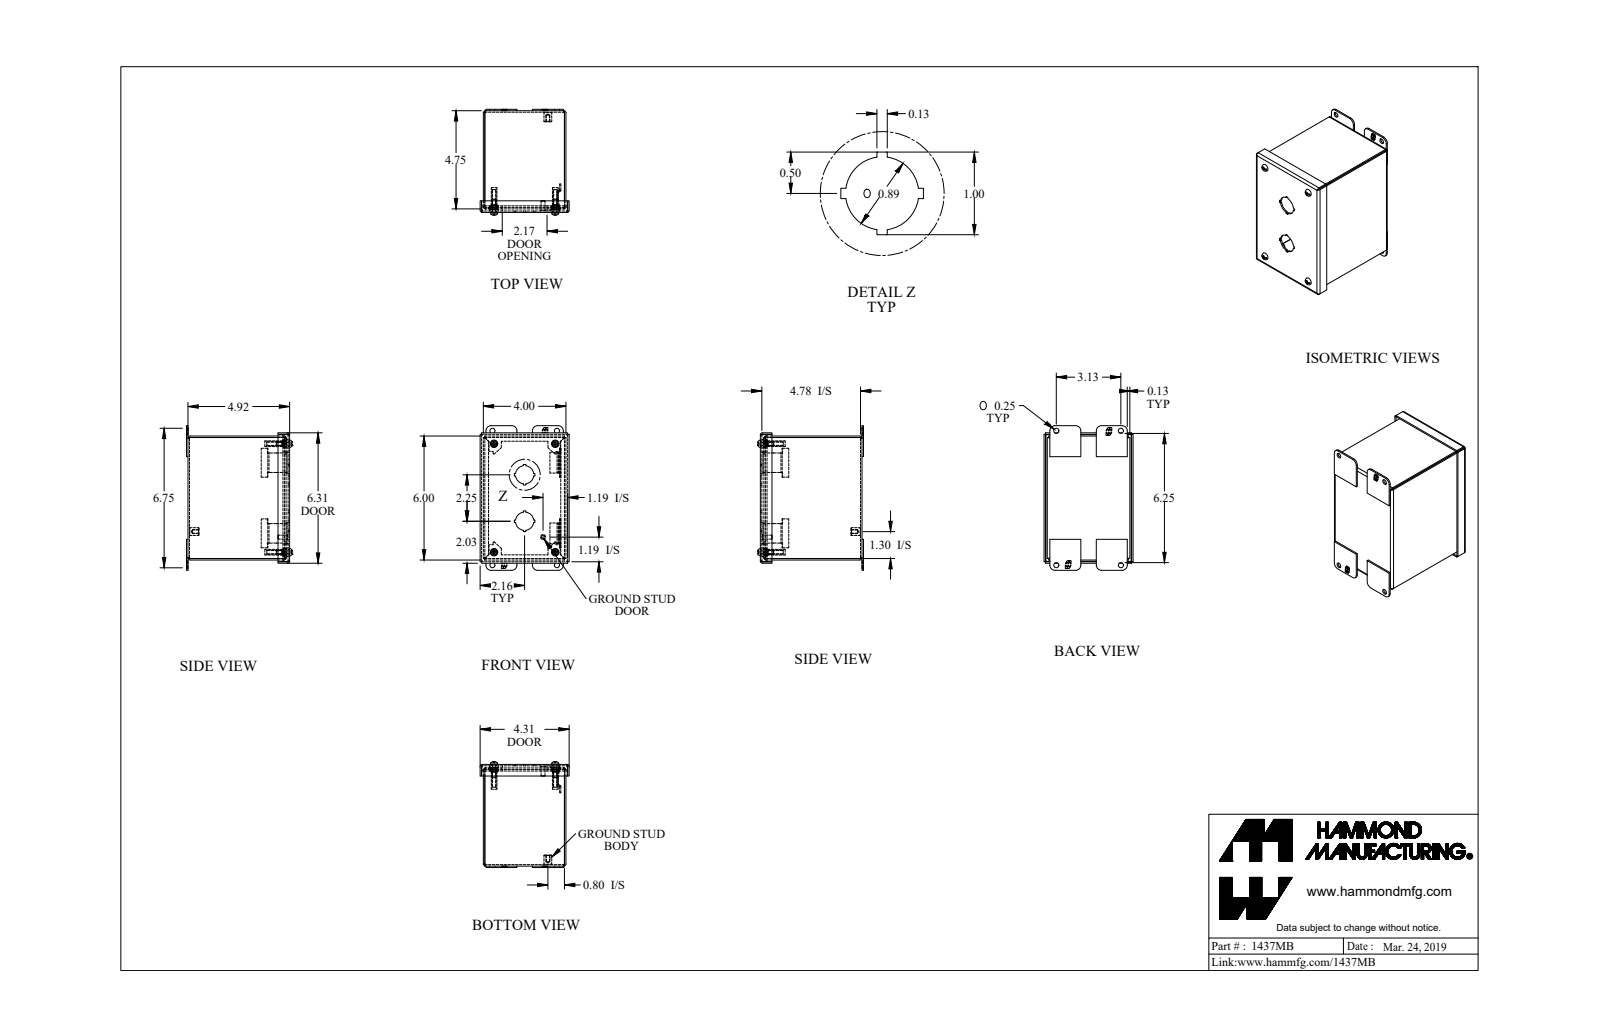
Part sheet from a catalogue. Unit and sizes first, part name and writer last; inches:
Units: inches
Overall size (bounding box): 7 × 5.121 × 4.312
Round holes (diameter × count): ⌀0.25 ×8, ⌀0.159 ×4, ⌀0.406 ×4, ⌀0.886 ×2, ⌀0.156 ×1
Round bosses / shafts (diameter × count): ⌀0.39 ×4, ⌀0.275 ×4, ⌀0.19 ×4, ⌀0.148 ×4, ⌀0.375 ×1, ⌀0.25 ×1, ⌀0.188 ×1
Partial cylindrical surfaces — rounded edges, fillets, slot ends (radius × count): R0.036 ×12, R0.108 ×12, R0.25 ×8, R0.029 ×4, R0.086 ×4, R0.16 ×4, R0.171 ×4, R0.125 ×2
Main face-to-face distances: 0.072, 3.928, 4.85, 5.928, 4.922, 4, 3.856, 4.778, 0.156, 6
Hole centre spacings: 5.25, 5.875, 3.106, 0.631, 2.107, 2.961, 3.107, 4.031
Volume: 14.1 in³ · Surface area: 378.3 in²
Bodies: 23 solids, 747 faces (523 planar, 168 cylindrical, 56 other)
Part name (STEP PRODUCT): 1437MB_Default
STEP written by: SolidWorks 2019 (CONFIG_CONTROL_DESIGN)
